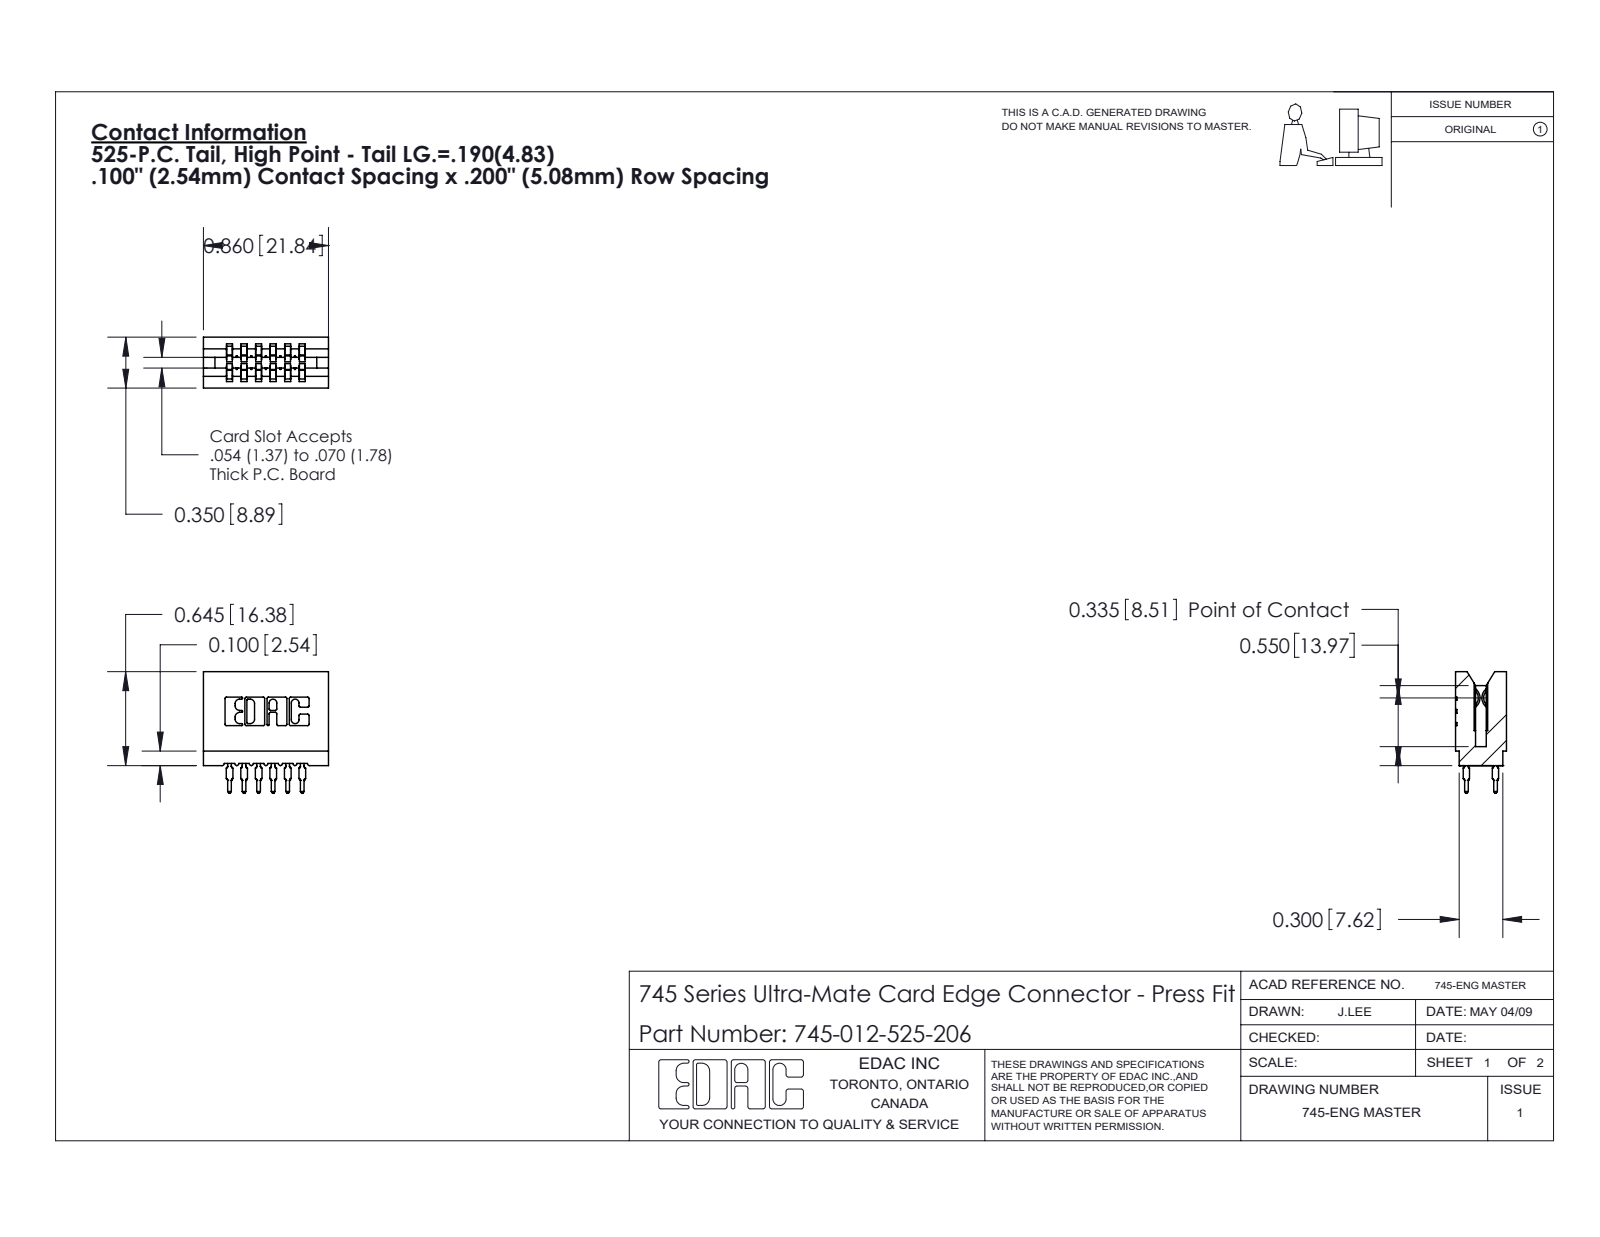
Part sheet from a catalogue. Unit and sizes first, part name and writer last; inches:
Units: inches
Overall size (bounding box): 0.86 × 0.836 × 0.35
Partial cylindrical surfaces — rounded edges, fillets, slot ends (radius × count): R0.021 ×24, R0.01 ×22, R0.015 ×12, R0.005 ×8, R0.011 ×8, R0.007 ×6, R0.031 ×6, R0.026 ×3
Main face-to-face distances: 0.1, 0.2, 0.042, 0.3, 0.142, 0.058, 0.242, 0.158, 0.4, 0.35
Volume: 0.132 in³ · Surface area: 5.536 in²
Bodies: 13 solids, 1170 faces (608 planar, 250 cylindrical, 312 other)
Part name (STEP PRODUCT): 745-292-001_525; 745-012-525-206; 745 Part_Insulator Option - 06
STEP written by: SolidWorks 2020 (CONFIG_CONTROL_DESIGN)
